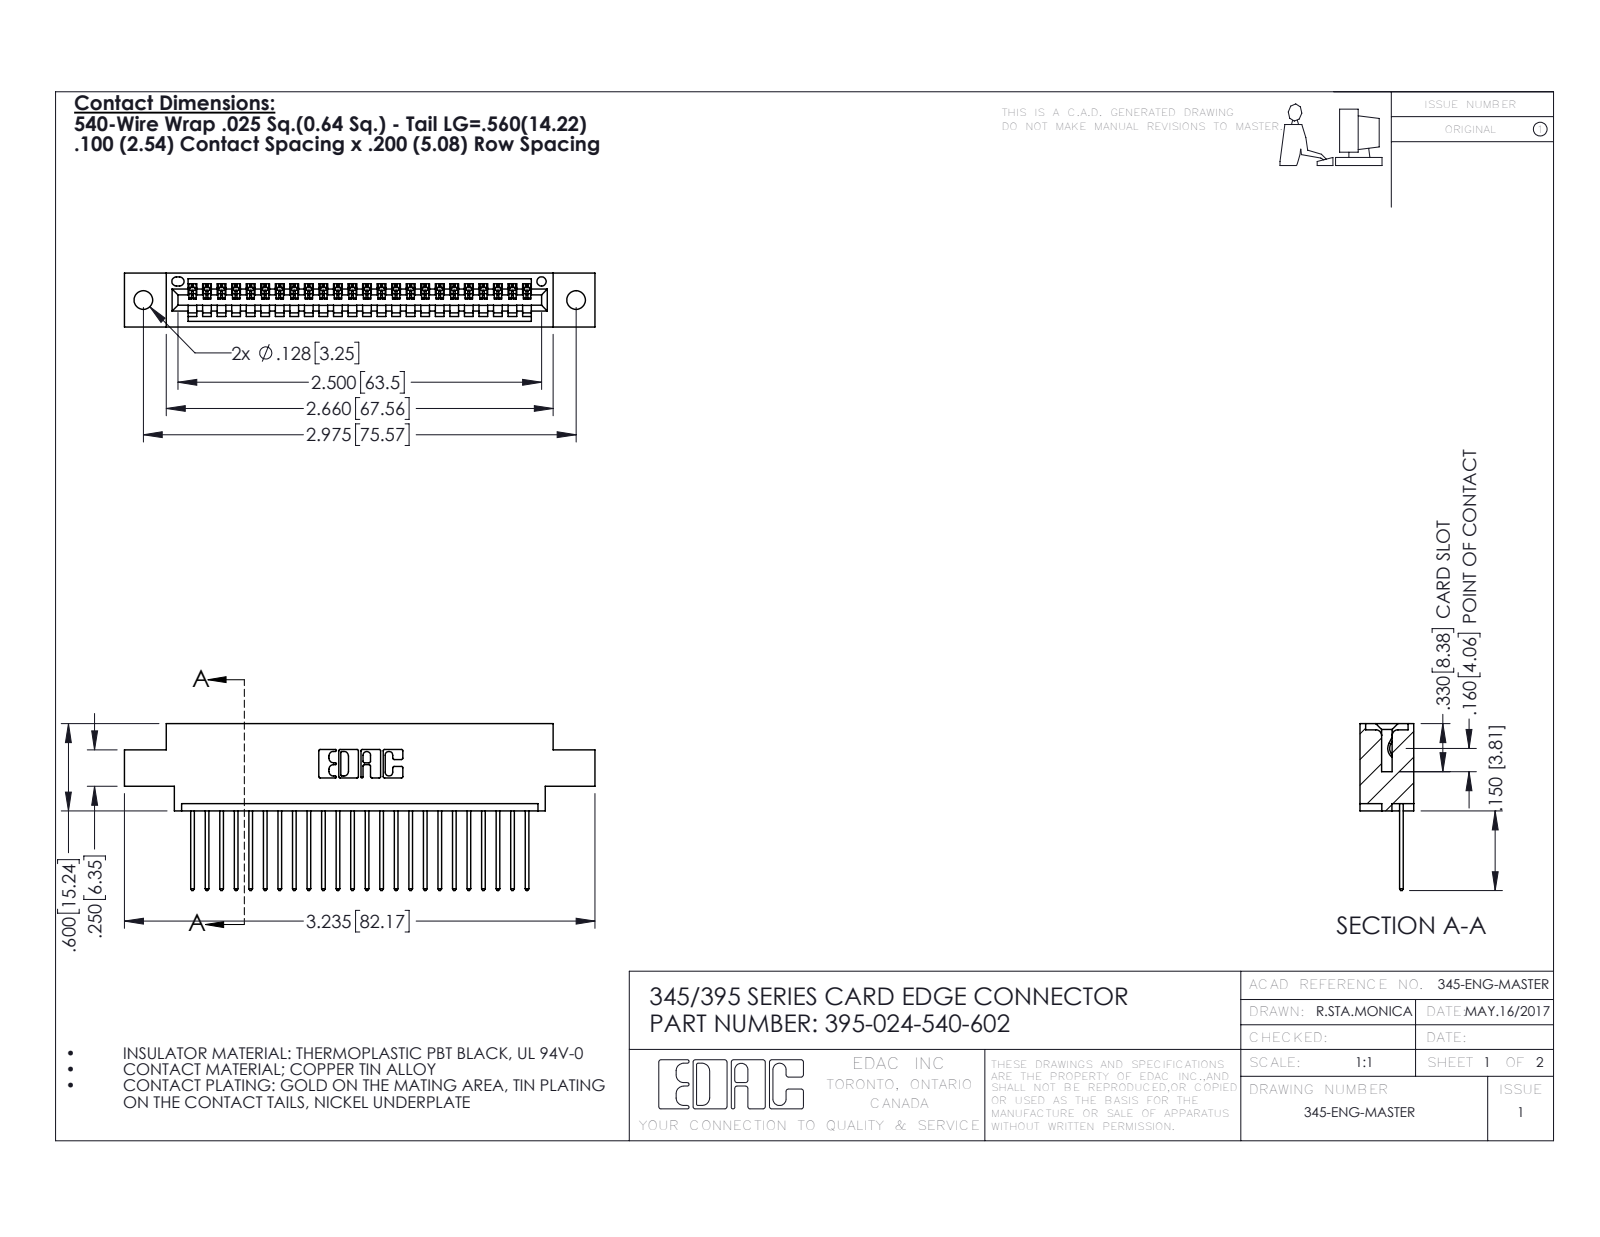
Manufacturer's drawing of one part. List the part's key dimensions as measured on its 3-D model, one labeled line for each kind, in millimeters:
Part name (STEP PRODUCT): 395-024-540-602; 345-292-001_345-293-140; 345 Part_0.170 Offset - 0.128 Dia
STEP written by: SolidWorks 2016 (CONFIG_CONTROL_DESIGN)
Units: millimetres
Bodies: 25 solids, 1522 faces (1044 planar, 478 cylindrical, 0 other)
Overall size (bounding box): 82.2 × 29.1 × 9.4
Volume: 7 540 mm³ · Surface area: 9 864 mm²
Round holes (diameter × count): ⌀3.3 ×2, ⌀1.6 ×1
Partial cylindrical surfaces — rounded edges, fillets, slot ends (radius × count): R0.2 ×48, R0.3 ×48, R0.3 ×22, R0.2 ×6, R0.8 ×6, R0.7 ×3, R0.8 ×2, R1 ×2
Main face-to-face distances: 7.6, 1.8, 9.4, 5.1, 2.5, 6.9, 0.6, 5.7, 4.4, 3.8
Hole centre spacings: 6.9, 69.6, 75.6
